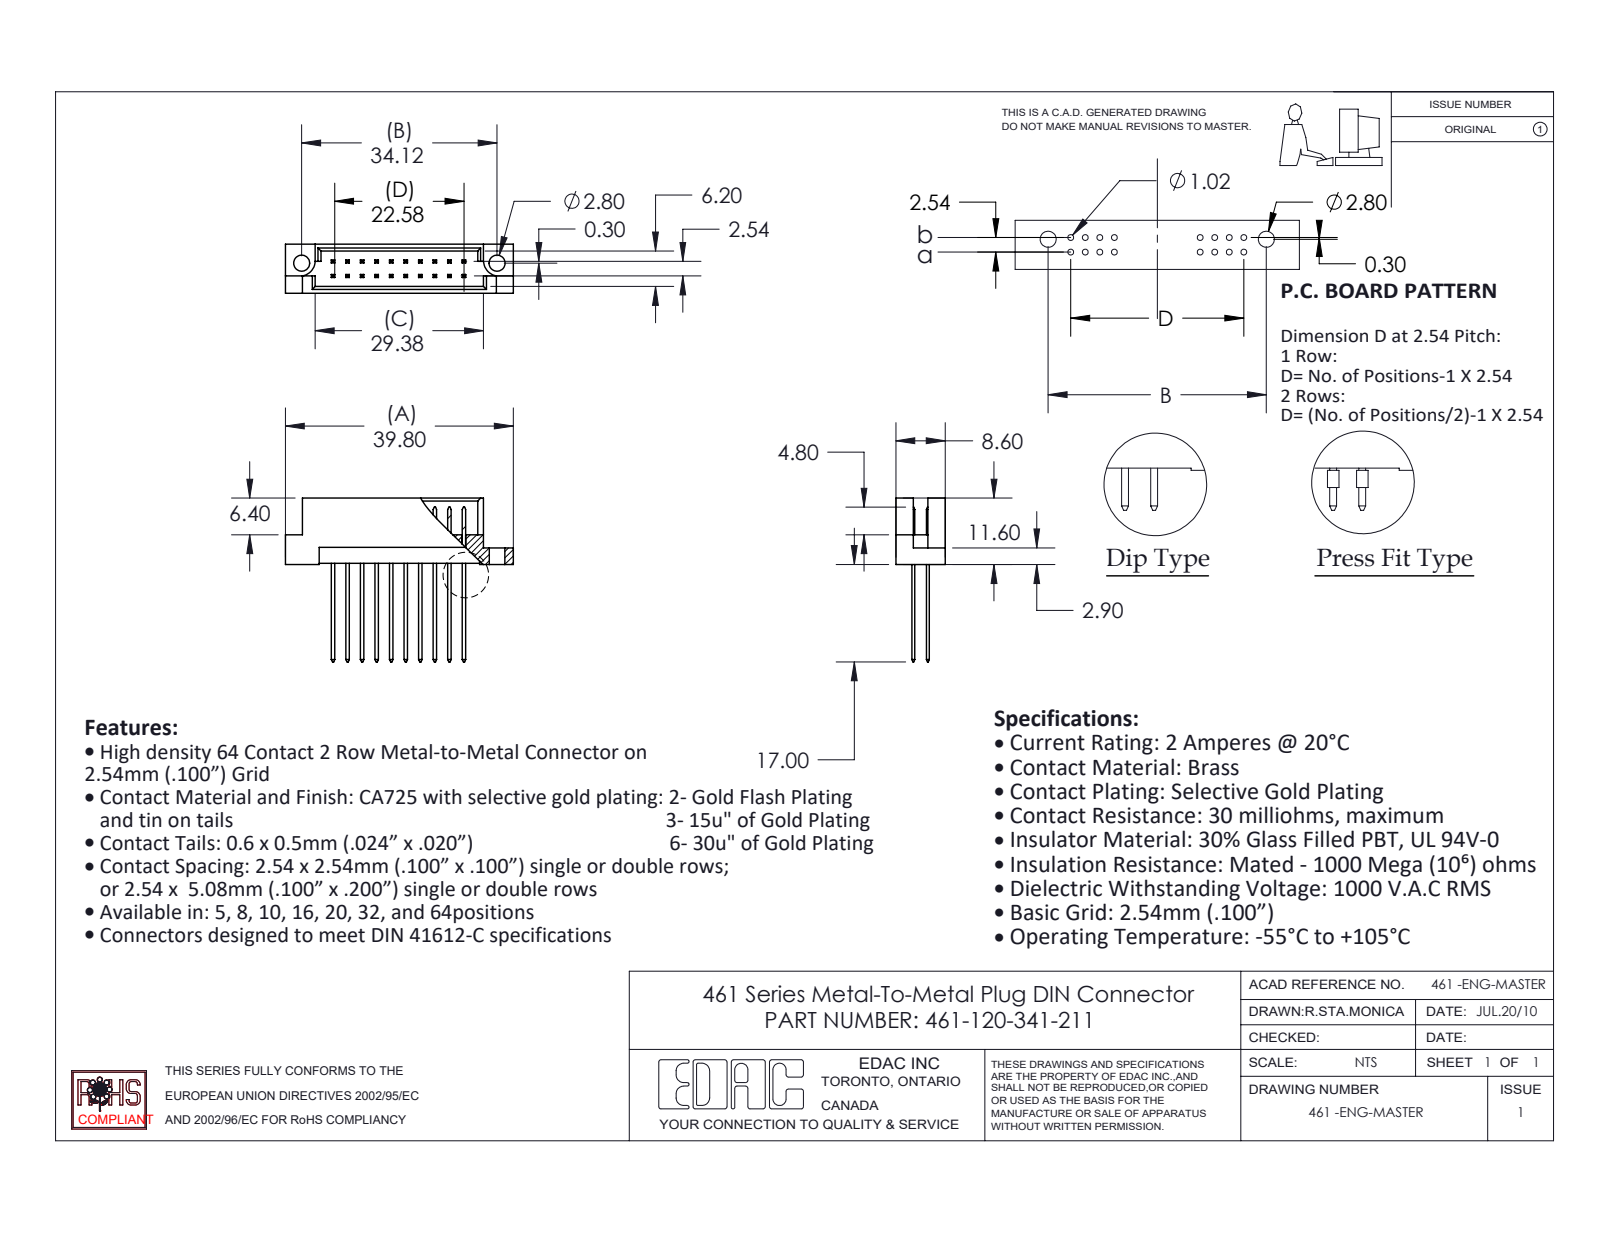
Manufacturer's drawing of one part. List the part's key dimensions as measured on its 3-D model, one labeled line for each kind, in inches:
Part name (STEP PRODUCT): 461 Part_20; 461-120-341-211; 461-290_41
STEP written by: SolidWorks 2020 (CONFIG_CONTROL_DESIGN)
Units: inches
Bodies: 21 solids, 408 faces (402 planar, 6 cylindrical, 0 other)
Overall size (bounding box): 1.567 × 1.126 × 0.339
Volume: 0.126 in³ · Surface area: 5.453 in²
Round holes (diameter × count): ⌀0.11 ×2
Partial cylindrical surfaces — rounded edges, fillets, slot ends (radius × count): R0.11 ×2
Main face-to-face distances: 0.1, 0.047, 0.291, 0.109, 0.129, 0.209, 0.229, 0.062, 0.082, 0.162
Hole centre spacings: 1.343
